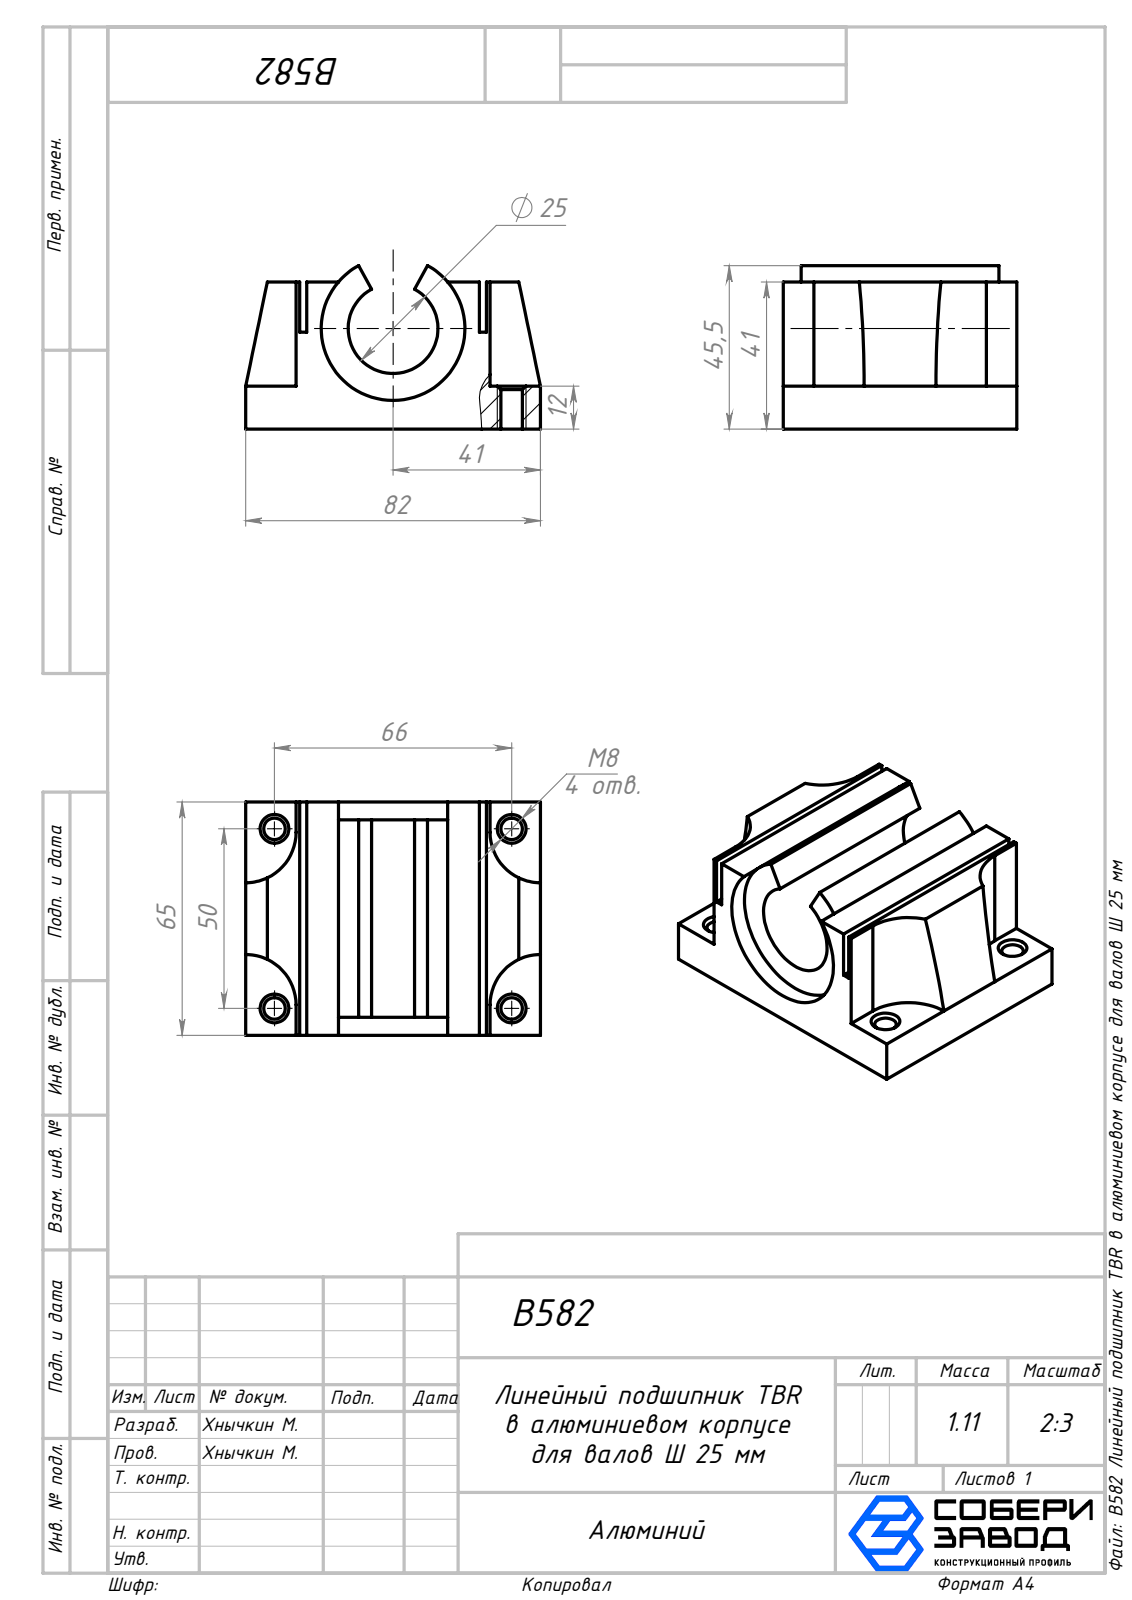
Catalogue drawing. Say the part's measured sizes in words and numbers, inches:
The part is named "B582 Линейный подшипник TBR в алюминиевом корпусе для валов Ø 25 мм". Its 3-D file was written by "SolidWorks 2026 (AUTOMOTIVE_DESIGN)". It is 1 solid with 60 faces: 29 planar, 23 cylindrical and 8 other. Overall it measures 3.228 by 2.559 by 1.793 inches. Its volume is 8.641 cubic inches and its surface area 44.82 square inches. Round holes: 4 of diameter 0.236, 1 of diameter 0.984, 1 of diameter 1.575. Partial cylindrical surfaces (rounded edges, fillets, slot ends): 4 of radius 0.551. The main face-to-face distances are 2.559, 0.591, 0.079, 1.969, 1.614, 0.669, 2.638, 0.197, 2.362, 0.551. The hole center spacings are 1.969, 2.598, 3.26.
